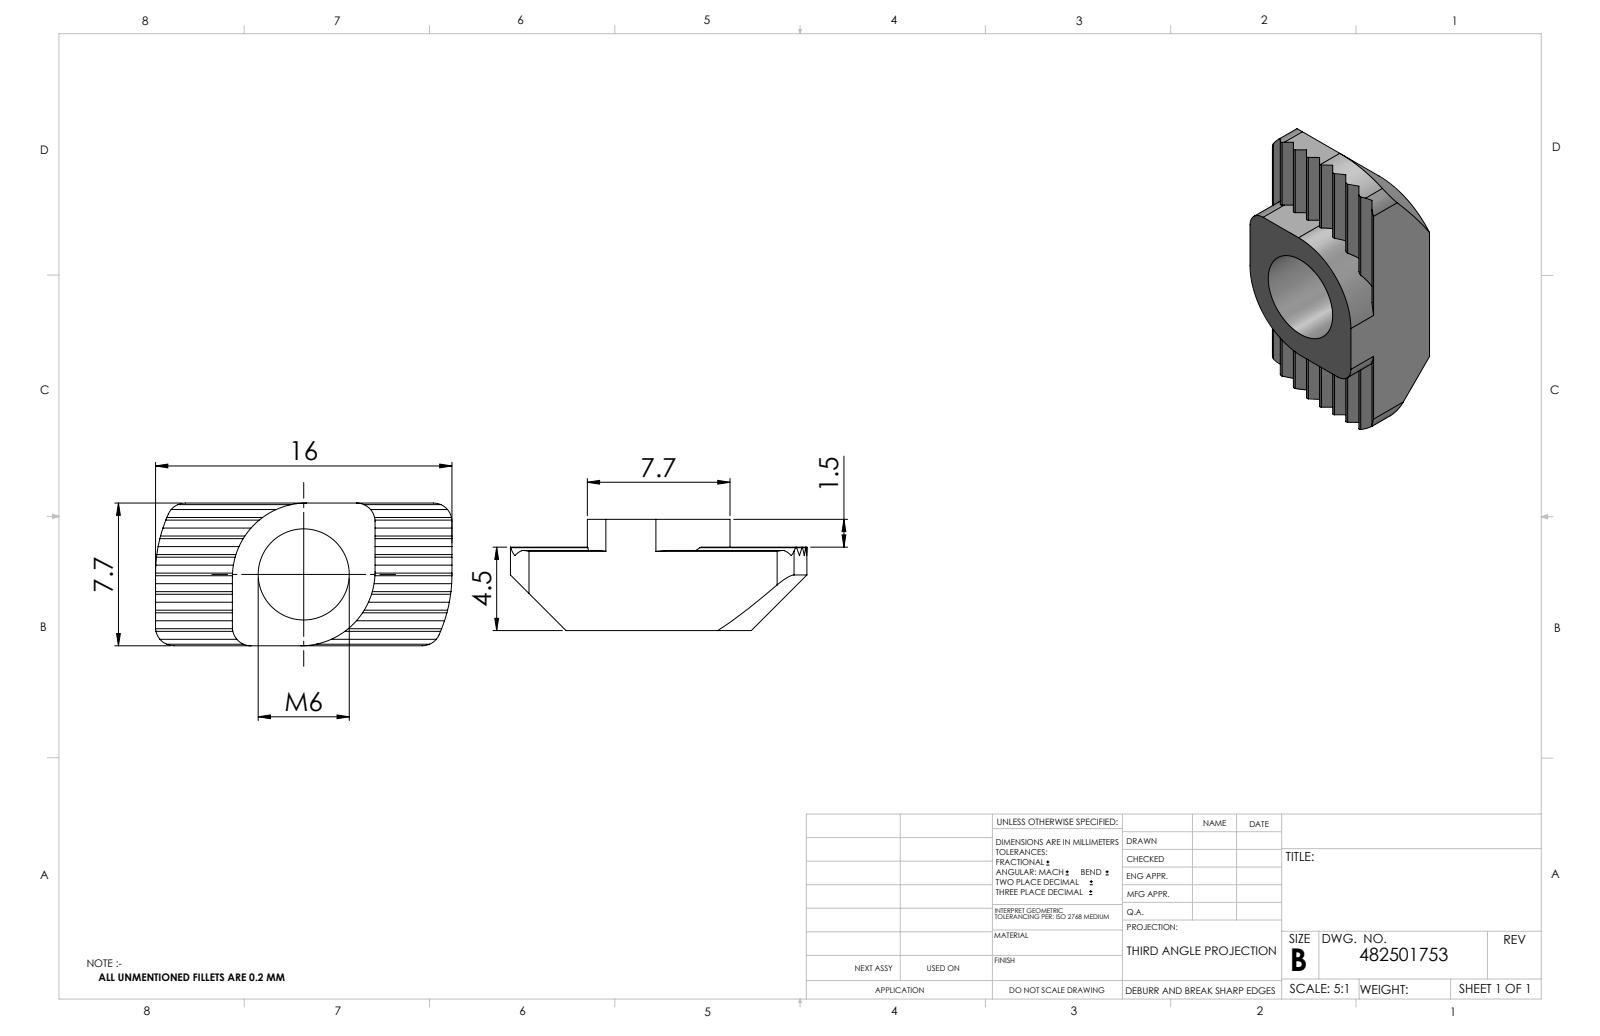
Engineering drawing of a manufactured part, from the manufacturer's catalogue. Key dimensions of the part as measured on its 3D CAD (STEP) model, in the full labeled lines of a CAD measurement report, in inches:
Part name (STEP PRODUCT): 482501753_c_1
STEP written by: SolidWorks 2014 (CONFIG_CONTROL_DESIGN)
Units: inches
Bodies: 1 solid, 74 faces (42 planar, 30 cylindrical, 2 other)
Overall size (bounding box): 0.63 × 0.303 × 0.236
Volume: 0.026 in³ · Surface area: 0.795 in²
Round holes (diameter × count): ⌀0.194 ×1
Partial cylindrical surfaces — rounded edges, fillets, slot ends (radius × count): R0.004 ×7, R0.039 ×6, R0.157 ×2, R0.315 ×1
Main face-to-face distances: 0.303, 0.028, 0.083, 0.056, 0.236, 0.111, 0.139, 0.028, 0.167, 0.056
